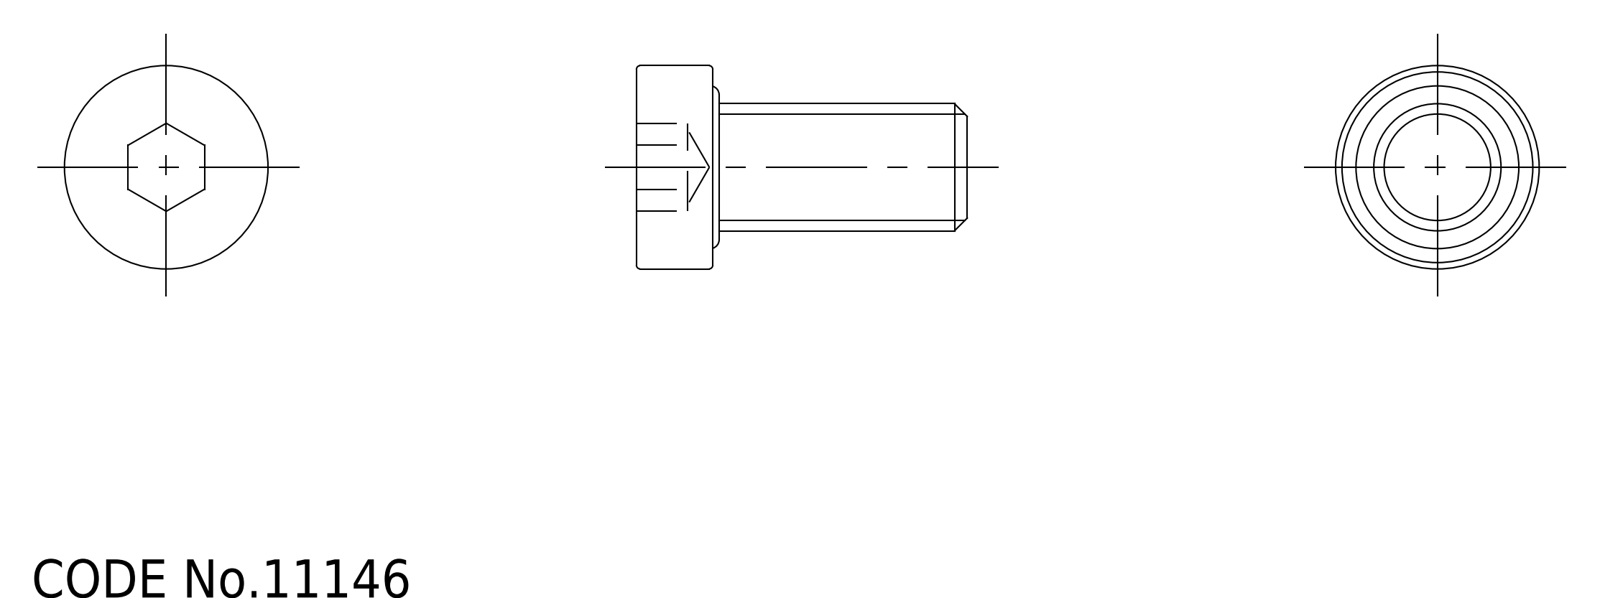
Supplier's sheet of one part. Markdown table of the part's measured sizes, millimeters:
| quantity | value |
| --- | --- |
| part name | screw; TL_418_M10_20 |
| STEP written by | SolidWorks 2015 (AUTOMOTIVE_DESIGN) |
| units | millimeters |
| bodies | 2 solids, 27 faces (11 planar, 6 cylindrical, 10 other) |
| overall size | 26 × 16 × 16 |
| volume | 2 603 mm³ |
| surface area | 1 611 mm² |
| round holes (diameter × count) | 15 × 1 |
| round bosses / shafts (diameter × count) | 16 × 1, 10 × 1 |
| main face-to-face distances | 5.1, 6, 26, 20.9, 4, 1.1, 22, 2, 0.9, 20 |
